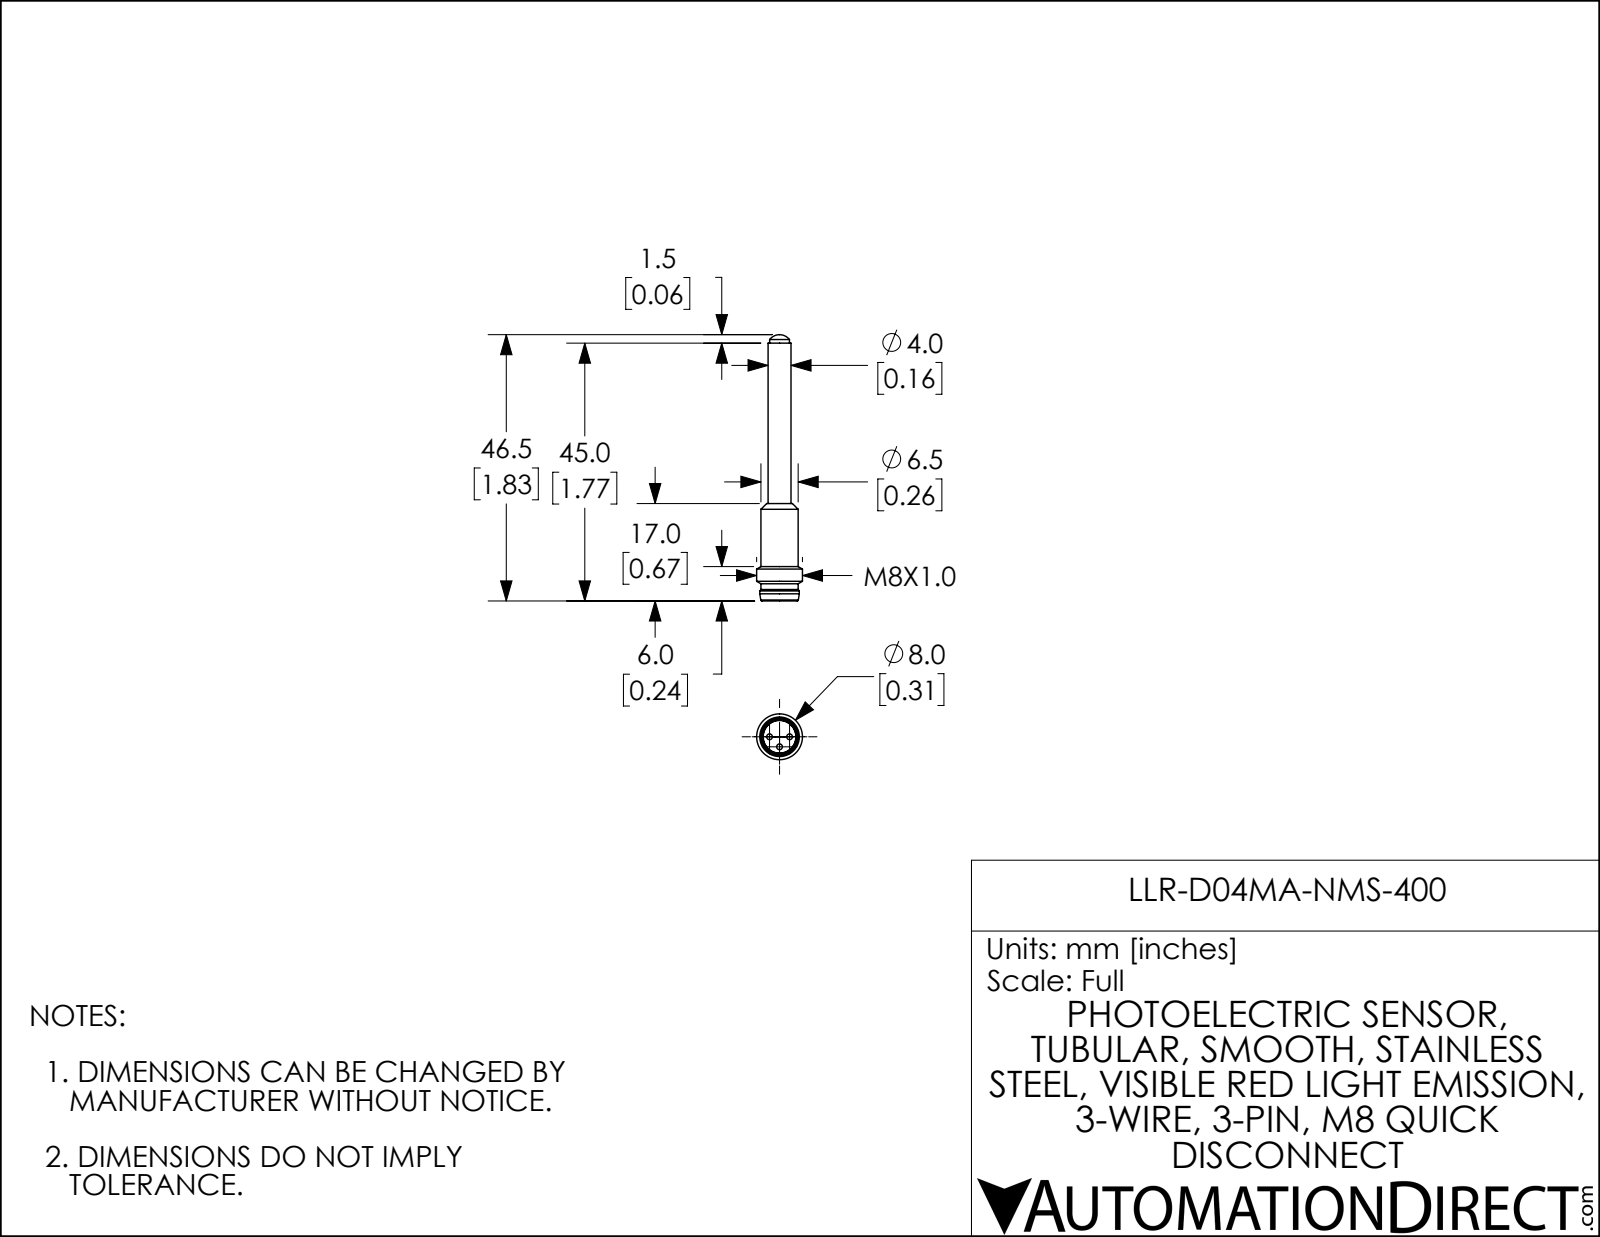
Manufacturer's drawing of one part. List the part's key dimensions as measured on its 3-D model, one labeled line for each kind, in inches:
Part name (STEP PRODUCT): LLR-D04MA-NxS-400
STEP written by: SolidWorks 2018 (AUTOMOTIVE_DESIGN)
Units: inches
Bodies: 1 solid, 27 faces (5 planar, 11 cylindrical, 11 other)
Overall size (bounding box): 1.83 × 0.315 × 0.315
Volume: 0.052 in³ · Surface area: 1.439 in²
Round holes (diameter × count): ⌀0.228 ×1
Round bosses / shafts (diameter × count): ⌀0.039 ×3, ⌀0.315 ×1, ⌀0.272 ×1, ⌀0.256 ×1, ⌀0.224 ×1, ⌀0.157 ×1, ⌀0.136 ×1
Main face-to-face distances: 0.476, 1.102, 1.578, 1.772, 0.669, 0.193, 1.575, 0.472, 0.197
